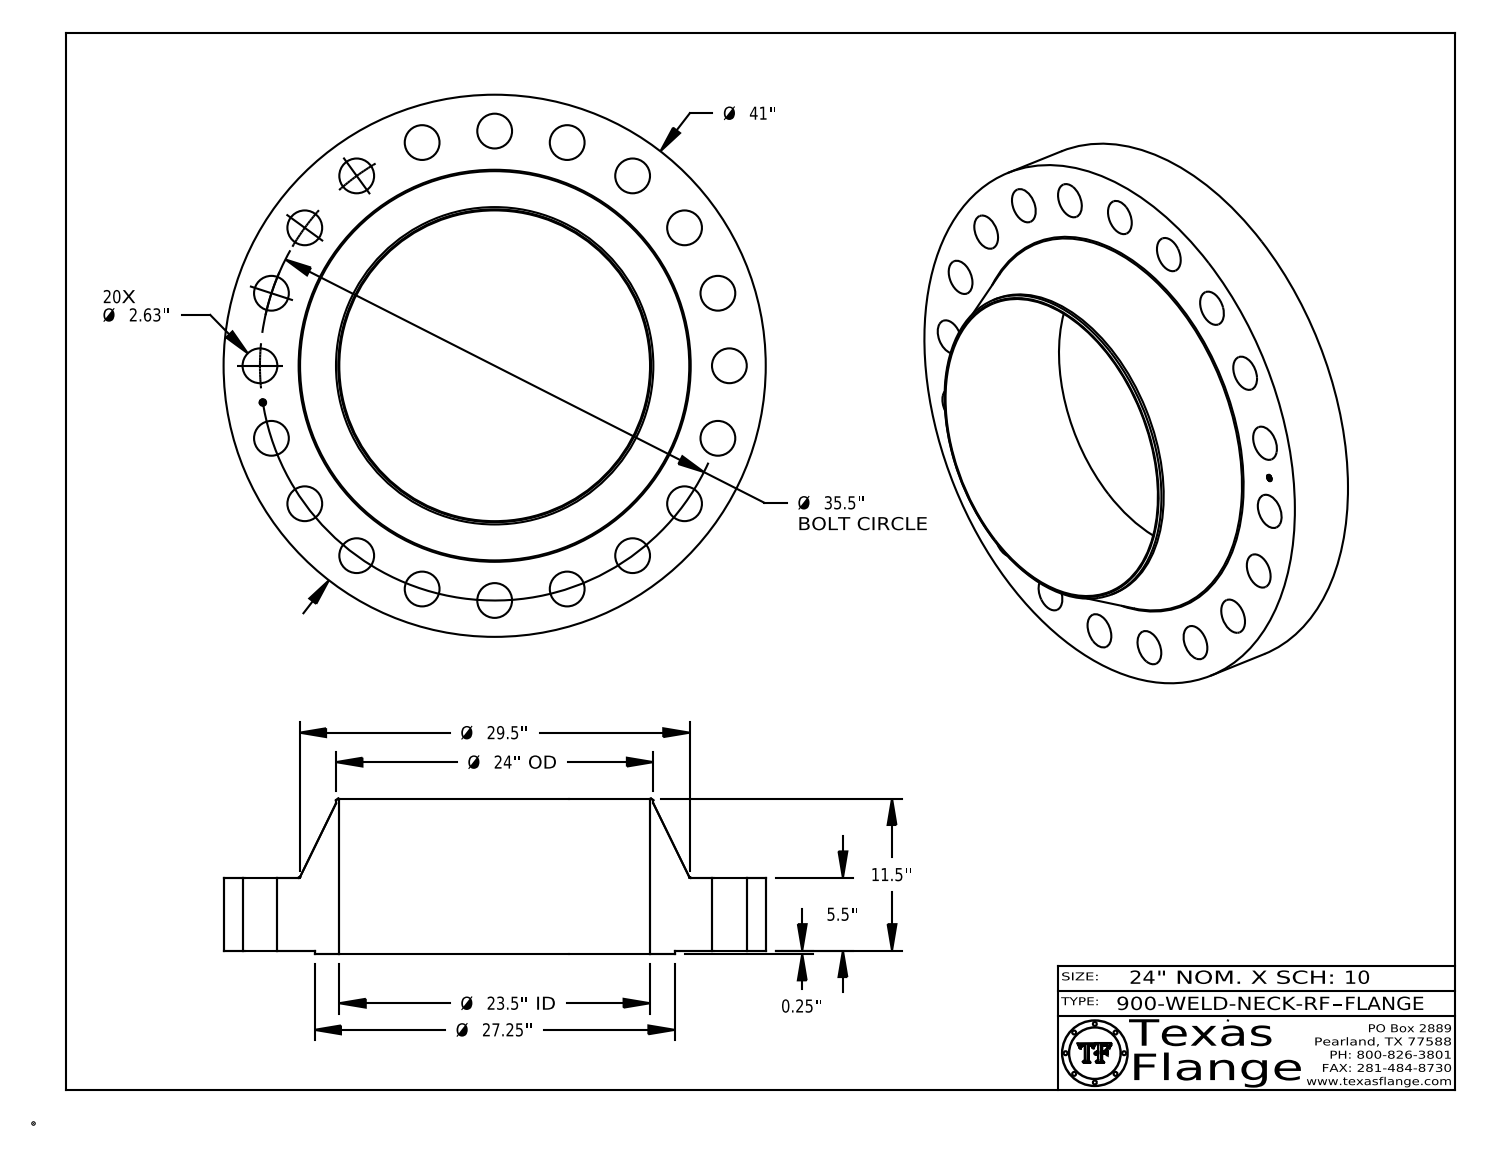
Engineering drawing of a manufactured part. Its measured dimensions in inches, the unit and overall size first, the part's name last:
Units: inches
Overall size (bounding box): 41 × 41 × 11.75
Round holes (diameter × count): ⌀2.63 ×20, ⌀0.495 ×1, ⌀23.5 ×1
Round bosses / shafts (diameter × count): ⌀0.03 ×8, ⌀41 ×1, ⌀27.25 ×1, ⌀24 ×1, ⌀0.39 ×1
Main face-to-face distances: 5.5, 0.25, 5.75, 11.75, 11.5, 6, 5.735, 5.485, 0.015, 6.015
Hole centre spacings: 17.75, 10.97, 28.72, 31.631, 16.117, 20.866, 25.102, 33.762
Volume: 5 055 in³ · Surface area: 4 377 in²
Bodies: 1 solid, 443 faces (369 planar, 68 cylindrical, 6 other)
Part name (STEP PRODUCT): 900-WELD-NECK-RF
STEP written by: CATIA V5 STEP AP214 (AUTOMOTIVE_DESIGN)
